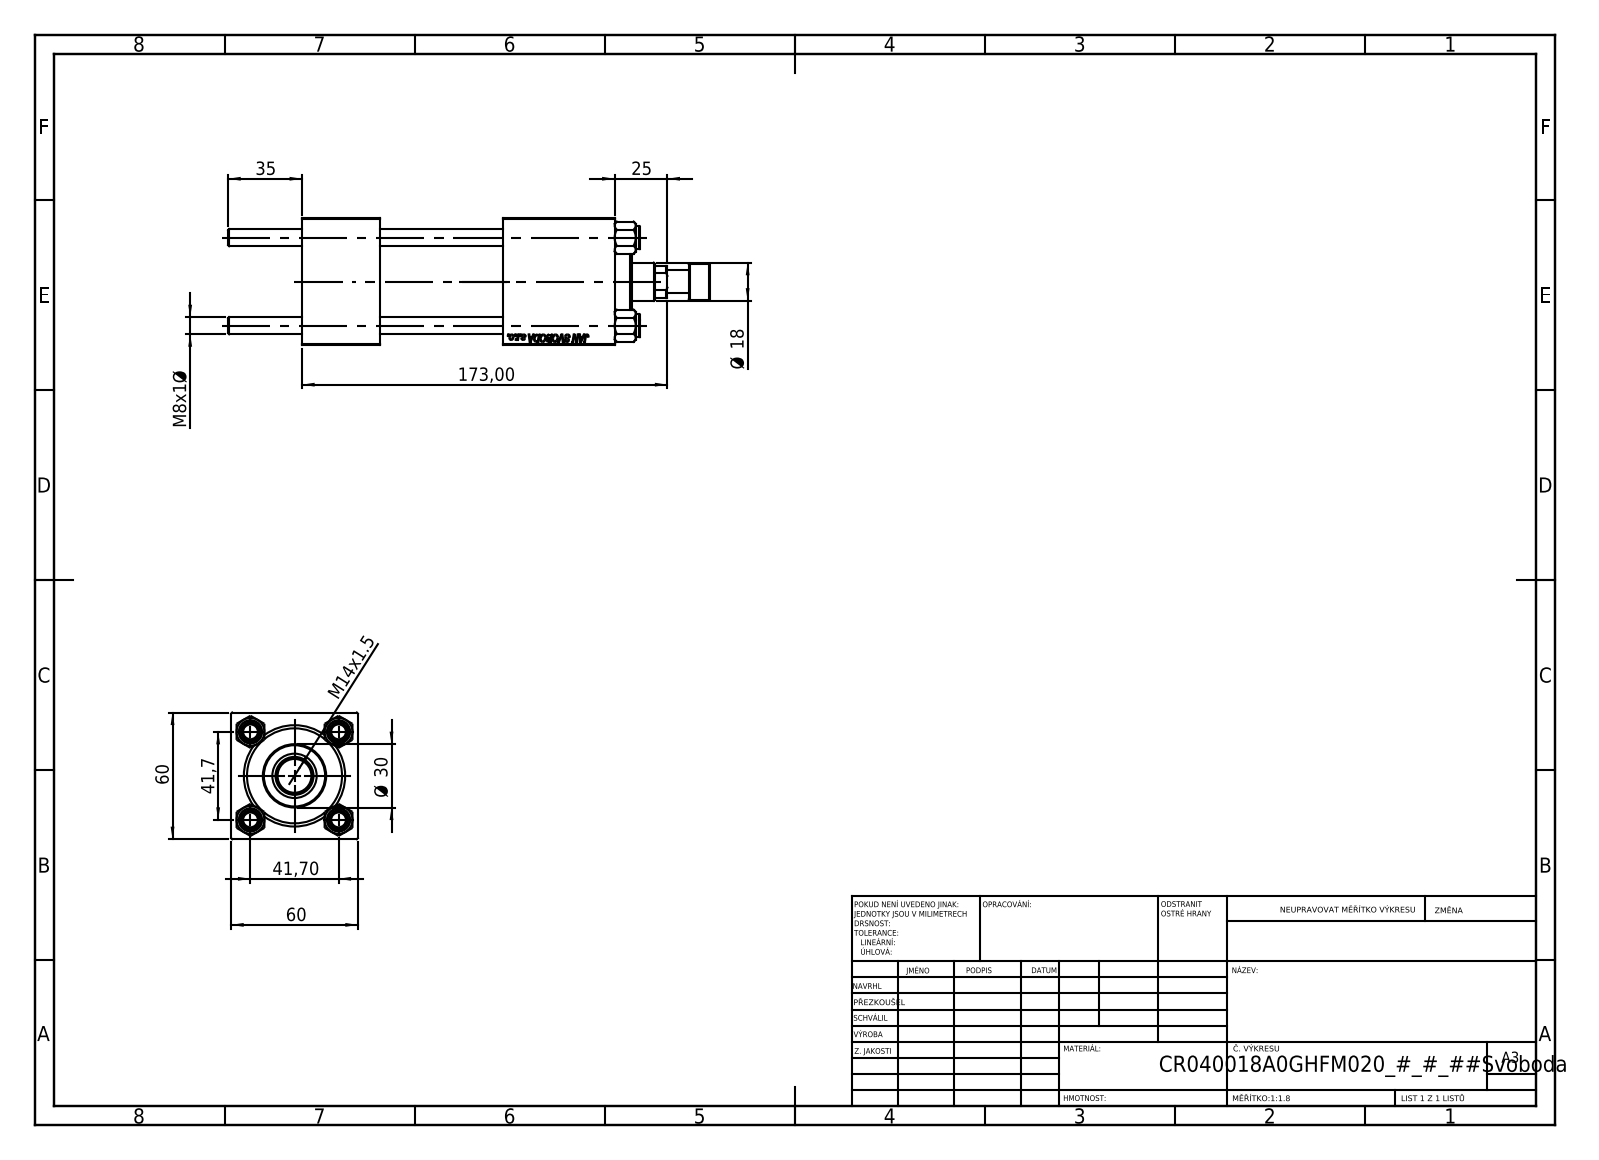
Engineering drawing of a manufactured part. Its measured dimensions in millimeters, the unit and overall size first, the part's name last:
Units: millimetres
Overall size (bounding box): 228 × 60 × 60
Round holes (diameter × count): ⌀8 ×4, ⌀7 ×2, ⌀16.66 ×2, ⌀24 ×2, ⌀8.5 ×1, ⌀18 ×1, ⌀21 ×1, ⌀31 ×1, ⌀40 ×1, ⌀45 ×1
Round bosses / shafts (diameter × count): ⌀11 ×5, ⌀46 ×1, ⌀30 ×1, ⌀17 ×1
Main face-to-face distances: 60, 37, 148, 111, 58, 53, 95, 119.3, 82.3, 24.3
Hole centre spacings: 29.49, 41.7, 58.97, 92.5
Volume: 417 114 mm³ · Surface area: 115 317 mm²
Bodies: 12 solids, 1146 faces (524 planar, 82 cylindrical, 540 other)
Part name (STEP PRODUCT): V215_VC_A; NUT_M5; V215CR_ROD_END_F; CR025_012_A_0_G_A_G_M_020_+#_##_TYCINKA (+2 more)
STEP written by: SolidWorks 2019 (CONFIG_CONTROL_DESIGN)
